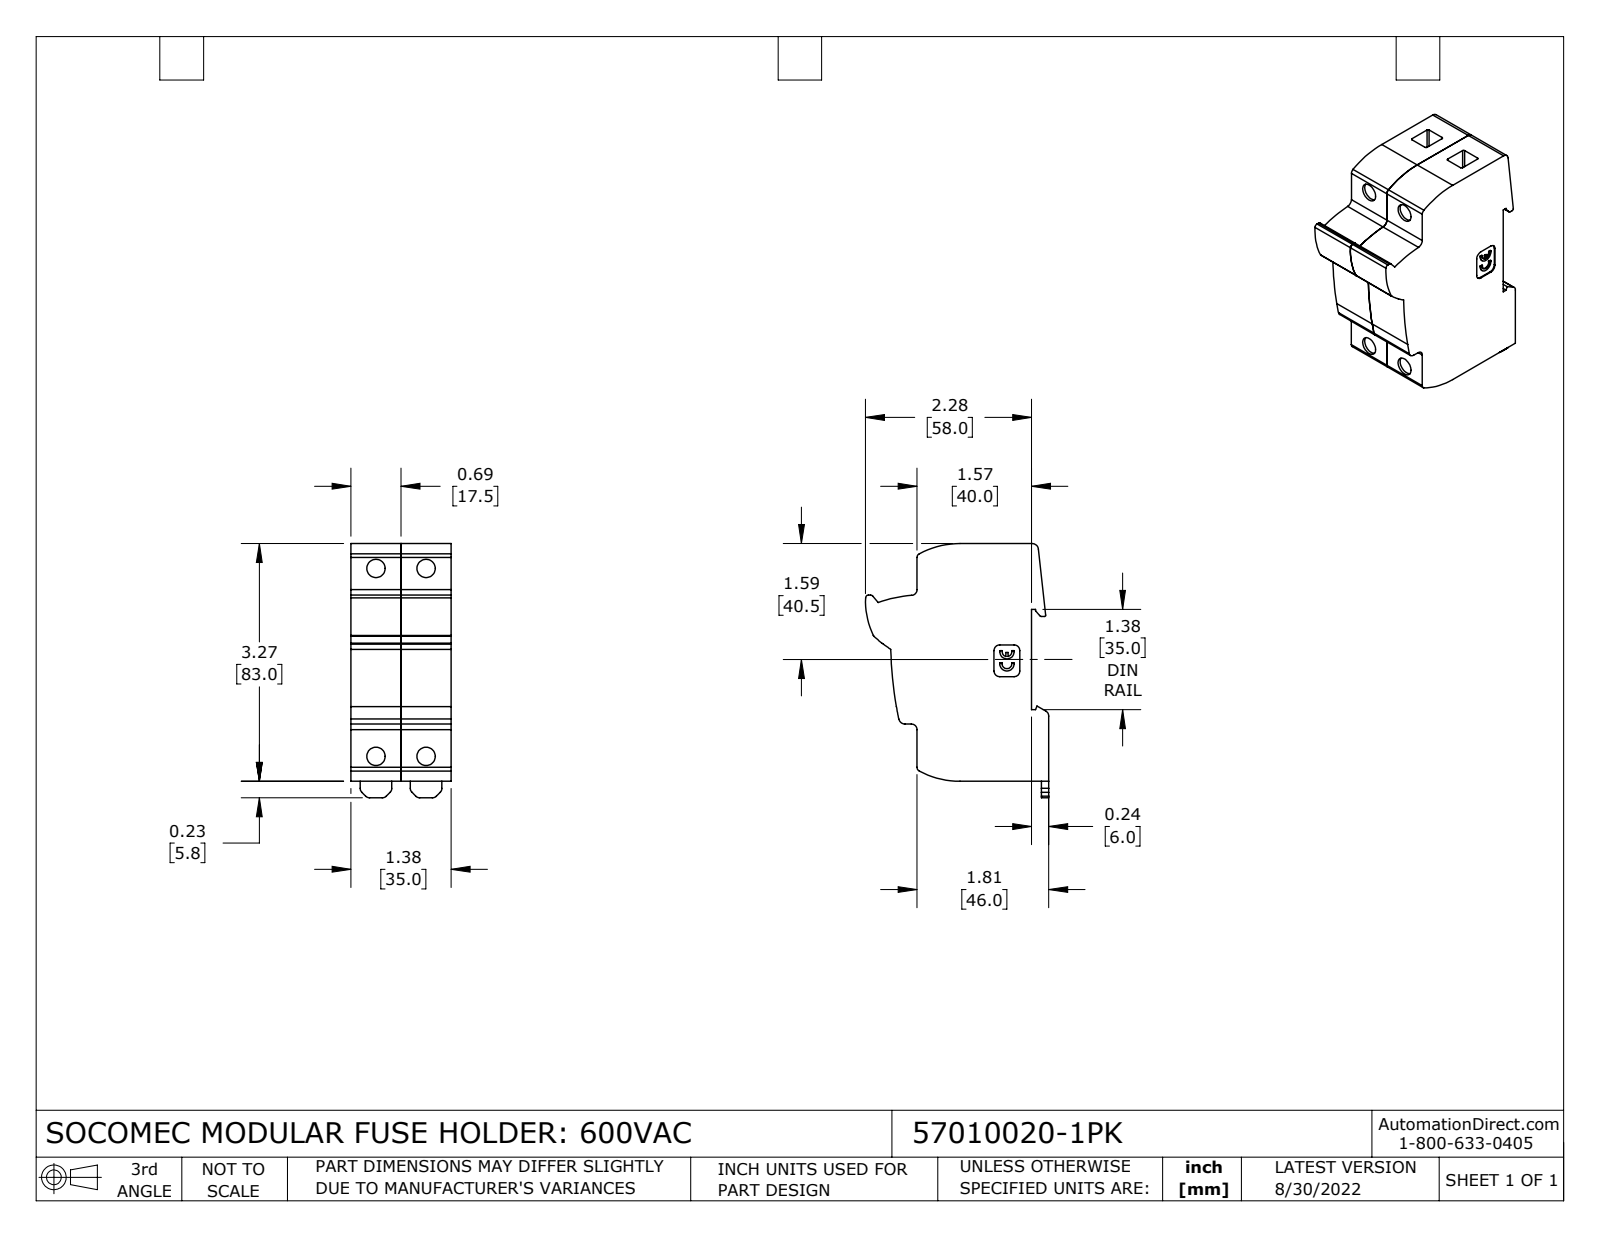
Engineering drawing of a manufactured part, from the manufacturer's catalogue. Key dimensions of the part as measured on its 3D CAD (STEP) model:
Part name (STEP PRODUCT): 57010020-1PK
STEP written by: SolidWorks 2021 (CONFIG_CONTROL_DESIGN)
Units: inches
Bodies: 2 solids, 210 faces (104 planar, 106 cylindrical, 0 other)
Overall size (bounding box): 3.496 × 2.52 × 1.378
Volume: 8.458 in³ · Surface area: 42.66 in²
Round holes (diameter × count): ⌀0.252 ×4
Partial cylindrical surfaces — rounded edges, fillets, slot ends (radius × count): R0.079 ×15, R0.02 ×9, R0.039 ×4, R0.059 ×2, R0.067 ×2, R0.087 ×2, R0.098 ×2, R1.186 ×2
Main face-to-face distances: 0.689, 1.378, 0.236, 1.575, 3.268, 1.811, 0.199, 0.49, 0.888, 1.179
Hole centre spacings: 0.689, 2.583, 2.673
